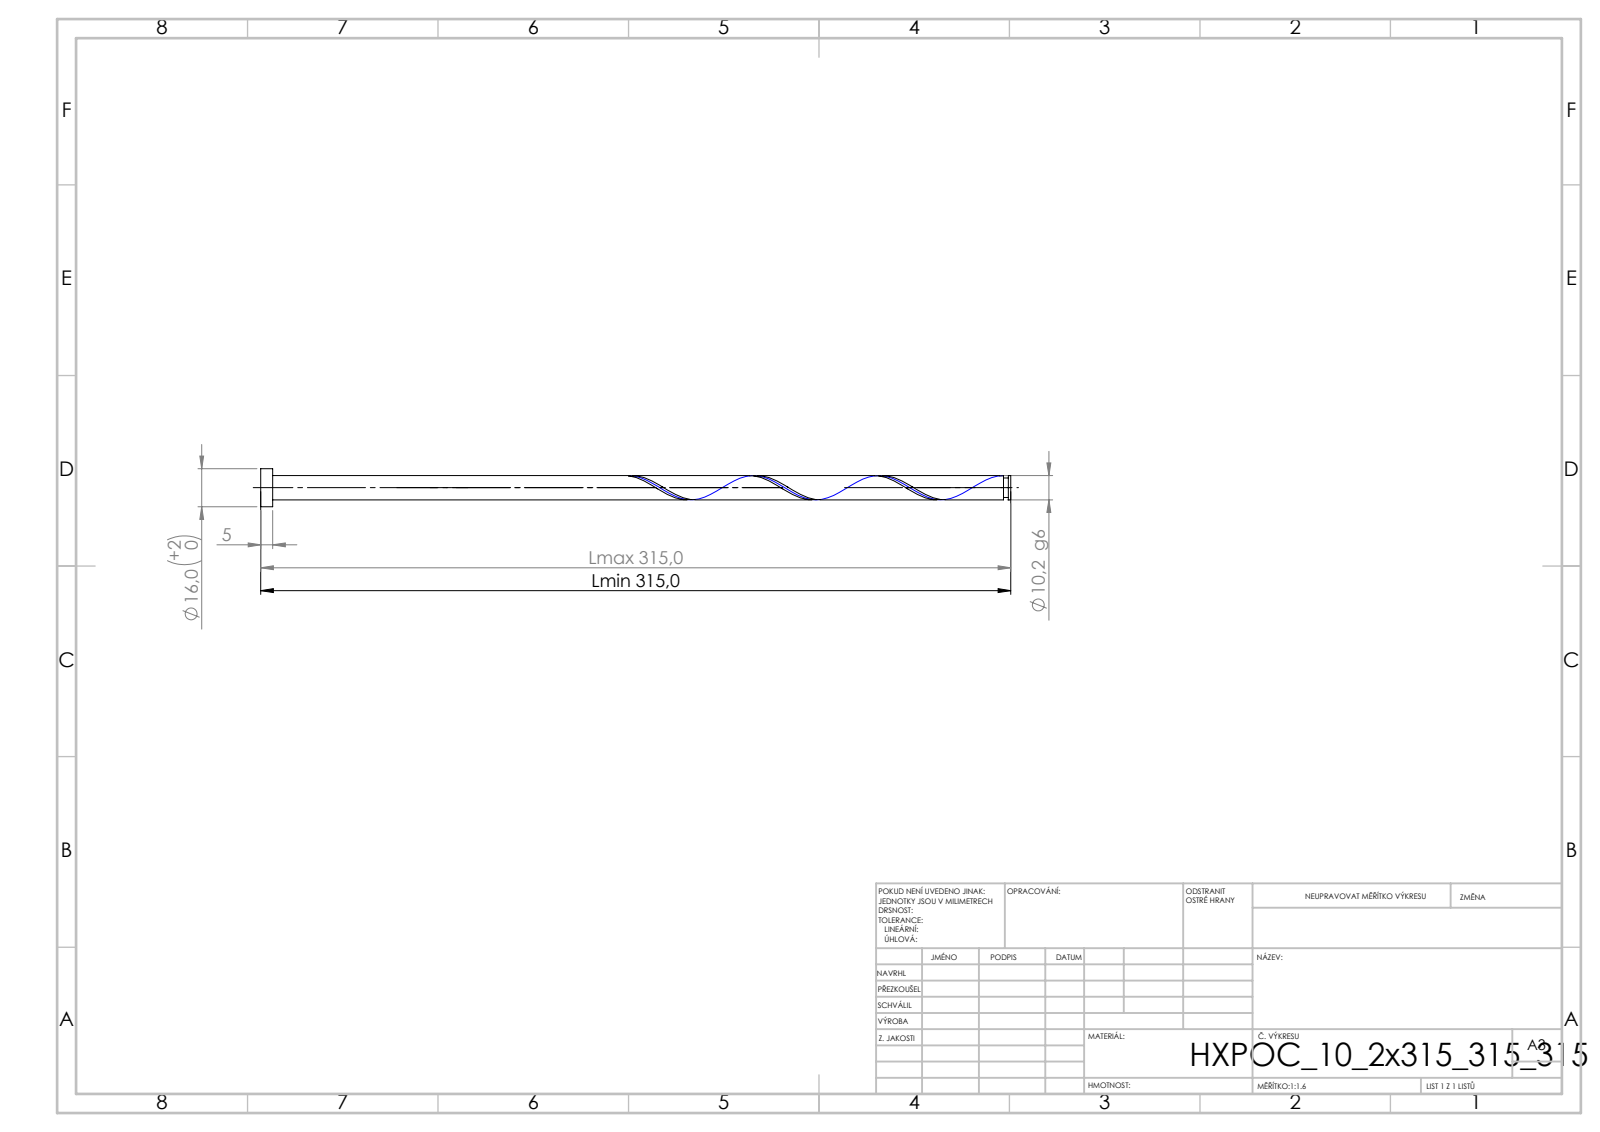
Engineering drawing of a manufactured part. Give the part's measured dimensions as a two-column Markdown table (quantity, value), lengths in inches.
| quantity | value |
| --- | --- |
| STEP written by | SolidWorks 2019 (CONFIG_CONTROL_DESIGN) |
| units | inches |
| bodies | 1 solid, 21 faces (6 planar, 14 cylindrical, 1 other) |
| overall size | 12.402 × 0.63 × 0.63 |
| volume | 1.588 in³ |
| surface area | 16.77 in² |
| round bosses / shafts (diameter × count) | 0.63 × 1, 0.402 × 1, 0.321 × 1 |
| main face-to-face distances | 0.197, 12.402, 12.205, 12.362, 12.165, 0.04, 12.281, 12.085, 0.08, 0.12 |
